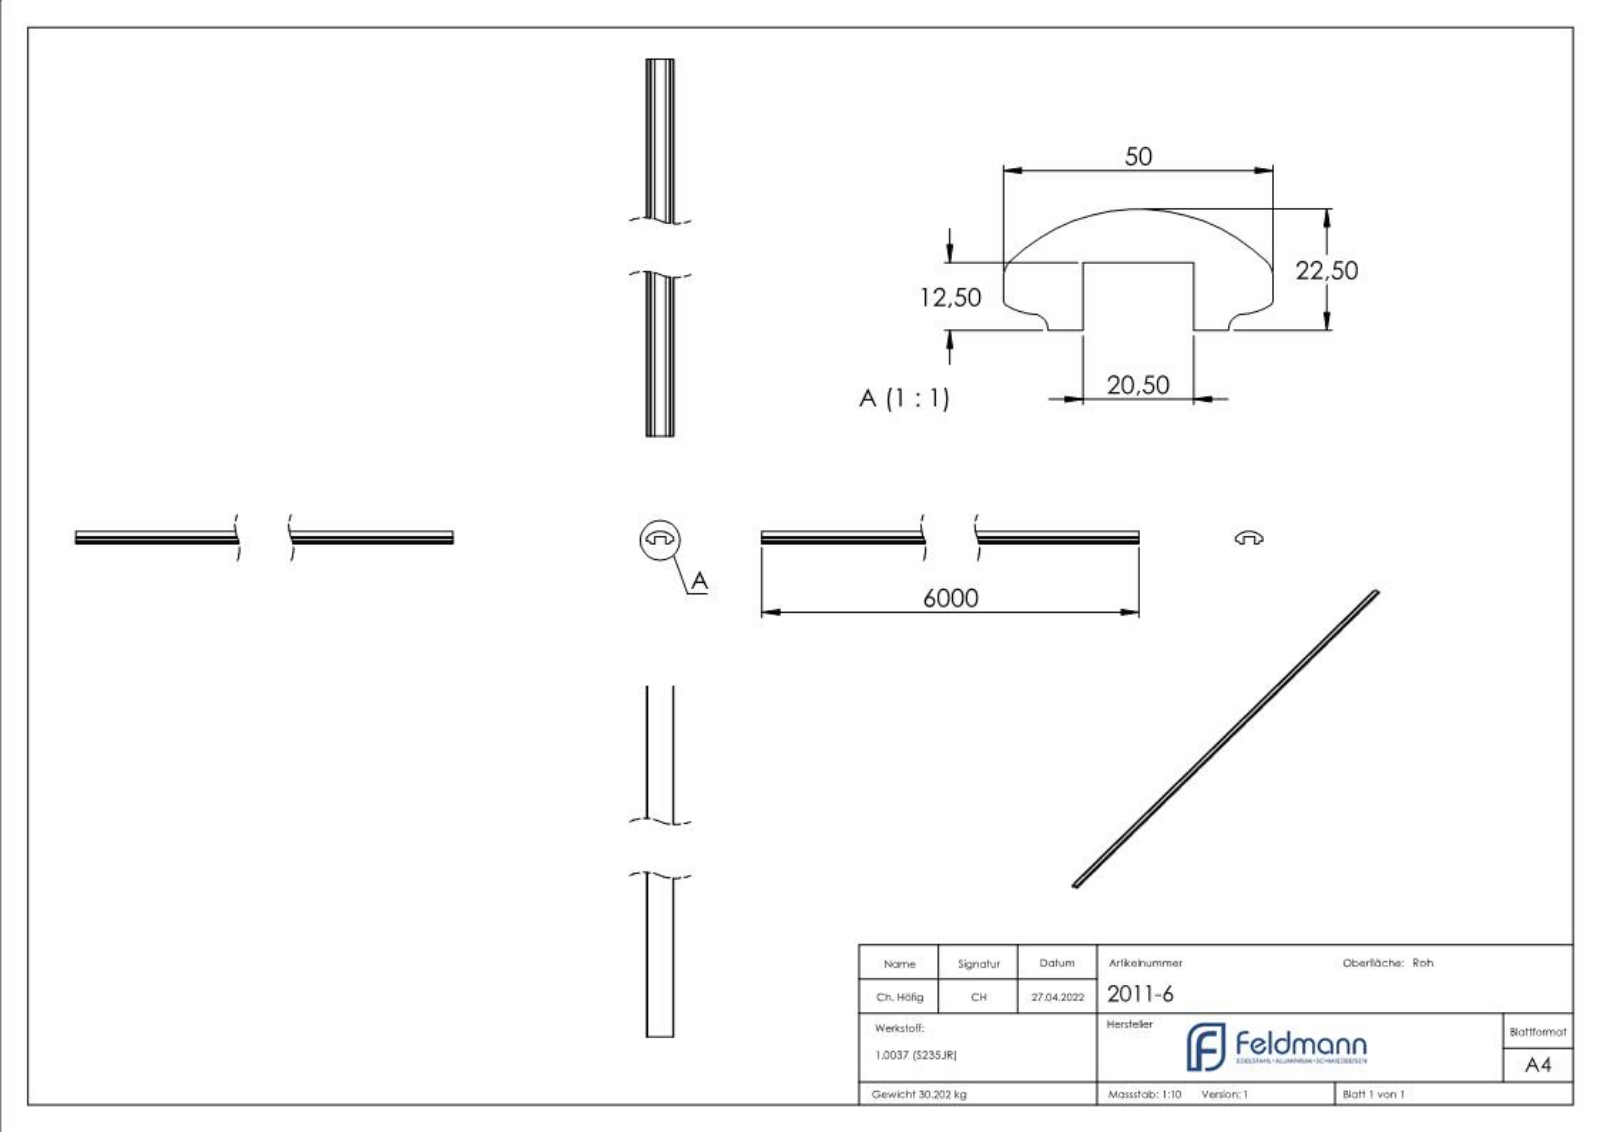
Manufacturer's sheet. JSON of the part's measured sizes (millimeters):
{"part_name": "2011-6", "step_written_by": "SolidWorks 2018 (CONFIG_CONTROL_DESIGN)", "units": "millimeters", "bodies": {"solids": 1, "faces": 233, "planar": 130, "cylindrical": 11, "other": 92}, "overall_size": [6000, 50, 22.5], "volume_mm3": 3872000, "surface_area_mm2": 890174, "partial_cylinders_radius": [[1, 4], [3.1, 2], [4, 2], [10.39, 2], [34, 1]], "face_to_face_distances": [12.5, 20.5, 14.75, 35.25, 50, 6000, 12.6, 1.14, 0.58, 1.01]}
